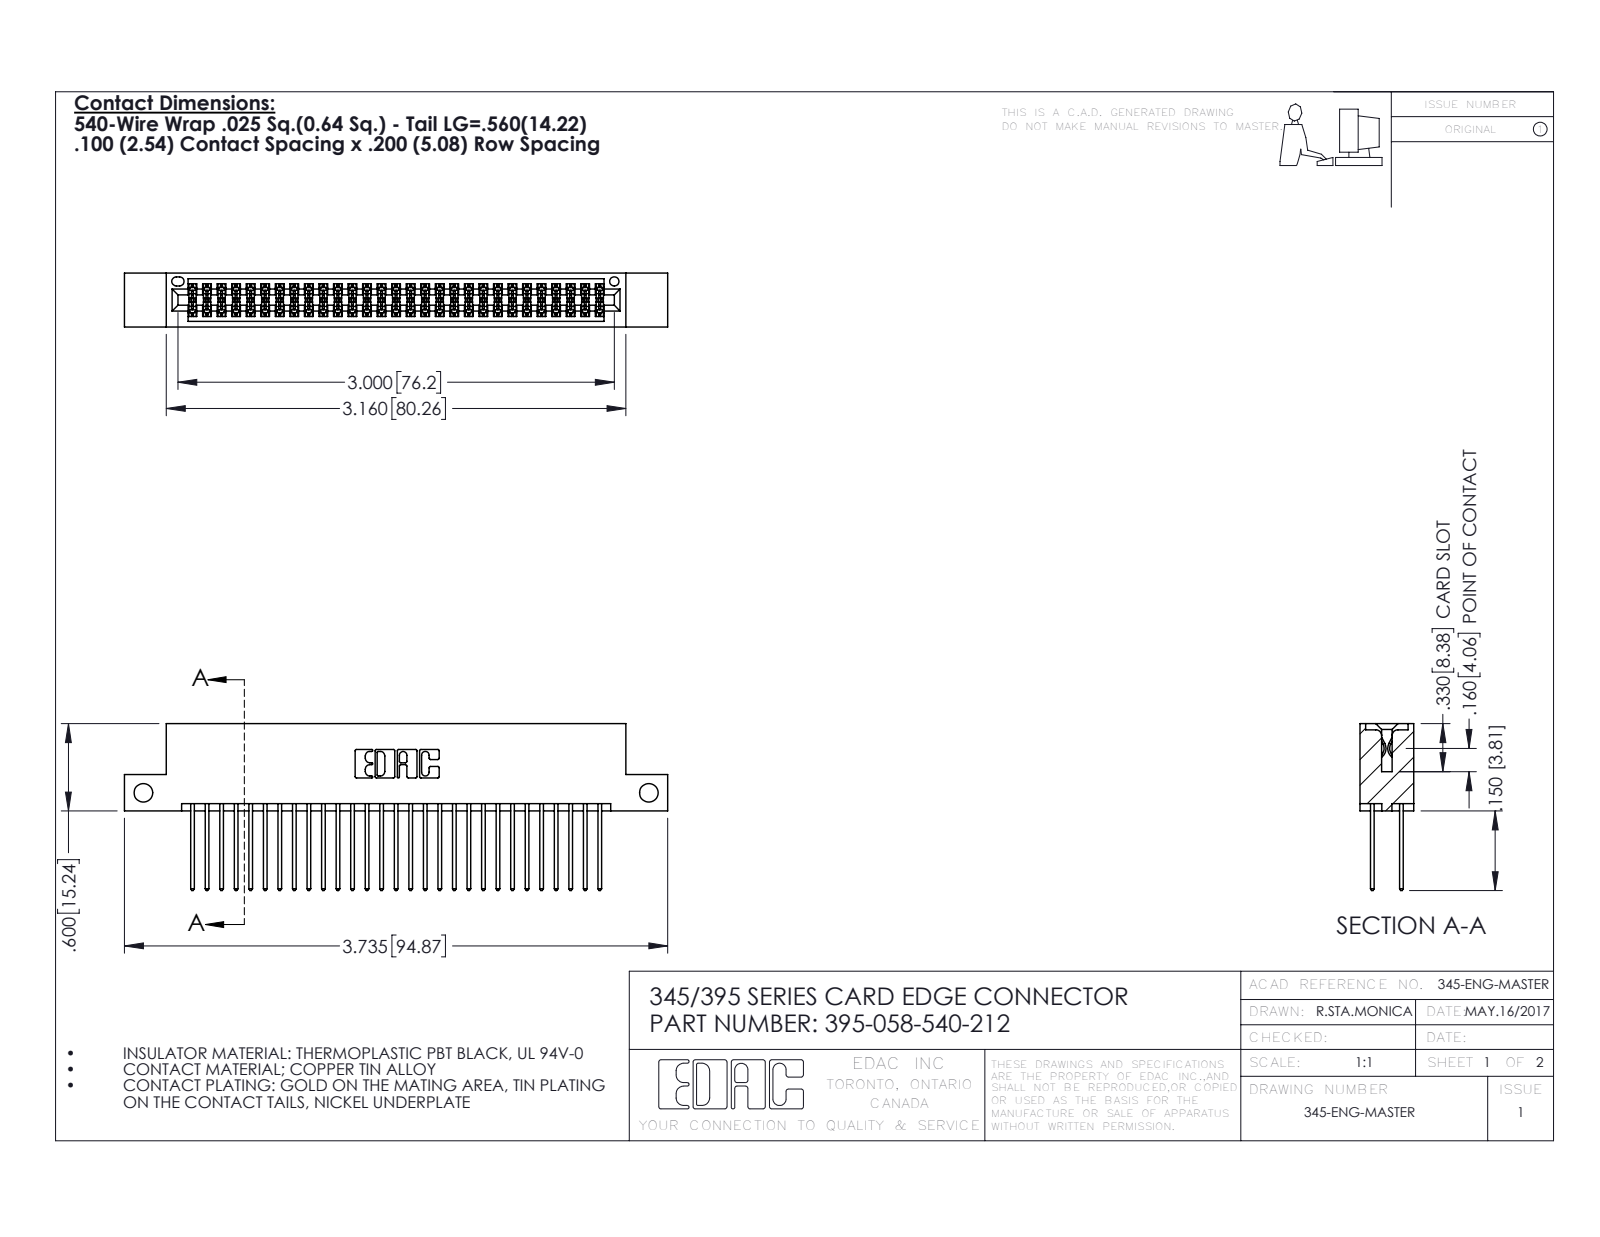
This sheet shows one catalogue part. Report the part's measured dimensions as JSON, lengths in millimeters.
{"part_name": "345-292-001_345-293-140; 345 Part_Flush Mounting Lugs - Side Mount; 395-058-540-212", "step_written_by": "SolidWorks 2016 (CONFIG_CONTROL_DESIGN)", "units": "millimeters", "bodies": {"solids": 59, "faces": 3026, "planar": 1994, "cylindrical": 1032, "other": 0}, "overall_size": [94.9, 29.1, 9.4], "volume_mm3": 9230, "surface_area_mm2": 14270, "round_holes": [[3.3, 2], [1.6, 1]], "partial_cylinders_radius": [[0.2, 87], [0.3, 58], [0.3, 22], [0.2, 6], [0.8, 6], [0.7, 3], [0.4, 2], [0.5, 2]], "face_to_face_distances": [7.6, 1.8, 5.1, 2.5, 6.9, 0.6, 9.4, 5.7, 4.4, 3.8], "hole_center_spacings": [88.3]}
